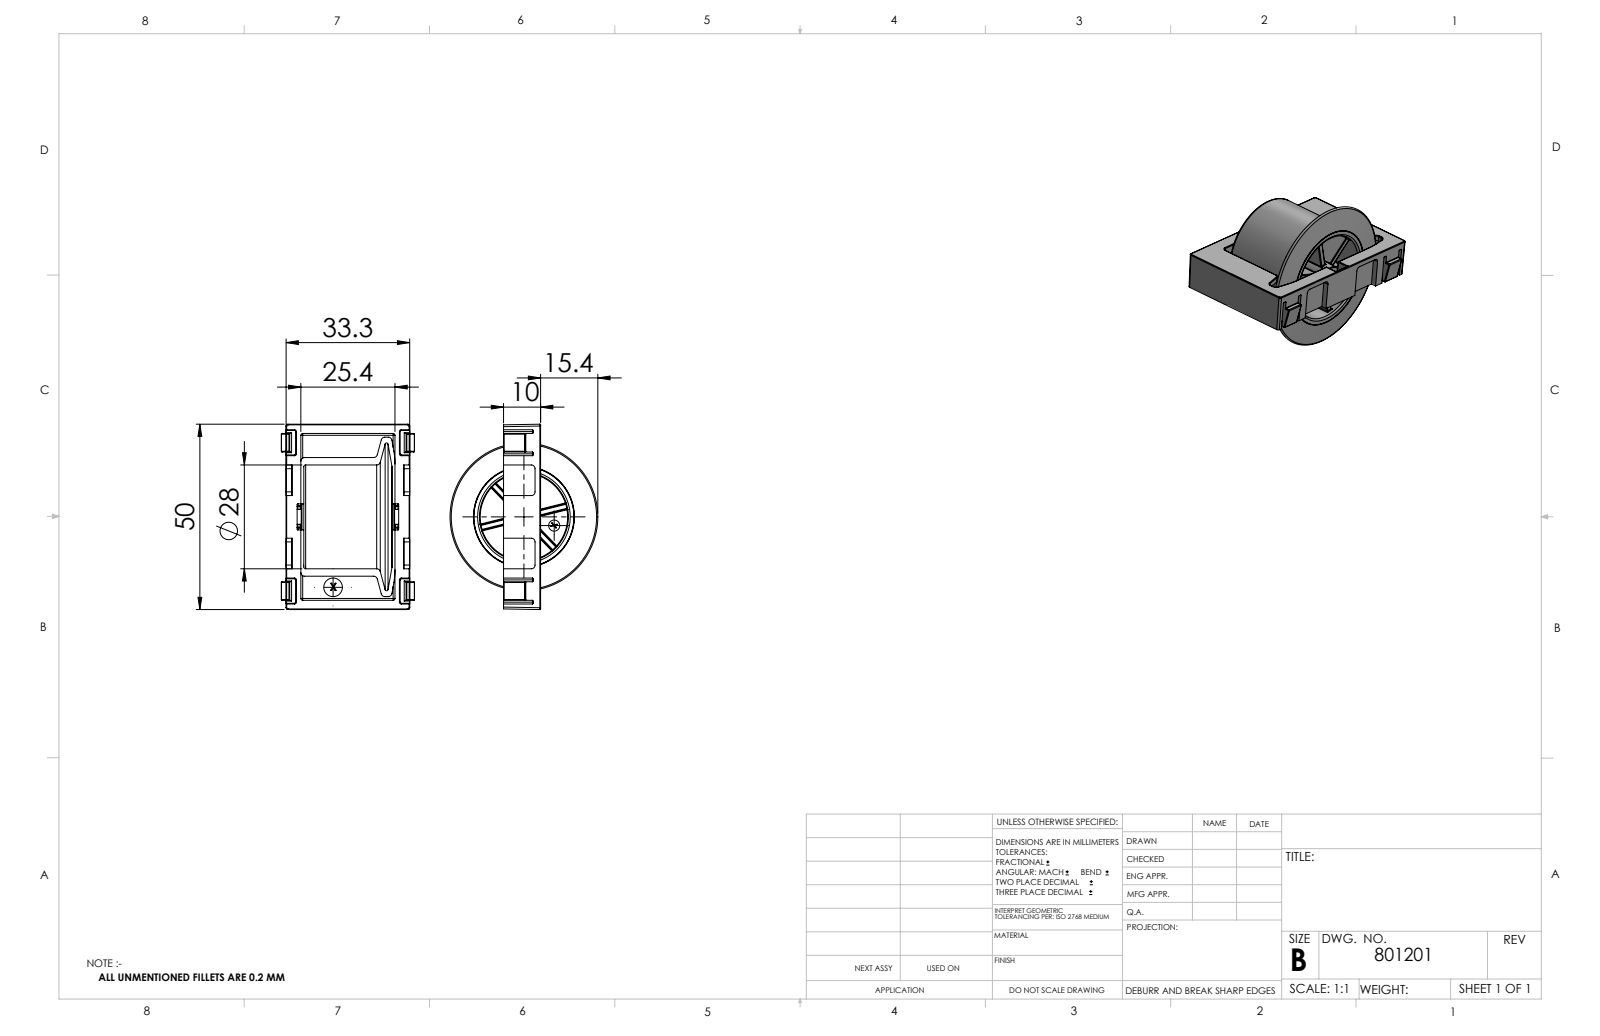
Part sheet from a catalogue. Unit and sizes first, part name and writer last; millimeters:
Units: millimetres
Overall size (bounding box): 49.99 × 39.89 × 35.9
Round holes (diameter × count): ⌀4.2 ×1, ⌀24 ×1
Round bosses / shafts (diameter × count): ⌀28 ×1, ⌀7 ×1, ⌀5.03 ×1, ⌀4 ×1, ⌀3 ×1
Partial cylindrical surfaces — rounded edges, fillets, slot ends (radius × count): R0.2 ×159, R0.5 ×22, R1 ×12, R0.1 ×2, R20 ×2, R2.05 ×1
Main face-to-face distances: 1.5, 11.8, 13.6, 1.8, 10, 1.51, 25.4, 14.8, 8.5, 2
Volume: 12 827 mm³ · Surface area: 14 072 mm²
Bodies: 3 solids, 805 faces (172 planar, 291 cylindrical, 342 other)
Part name (STEP PRODUCT): 801201_c_1
STEP written by: SolidWorks 2014 (CONFIG_CONTROL_DESIGN)
